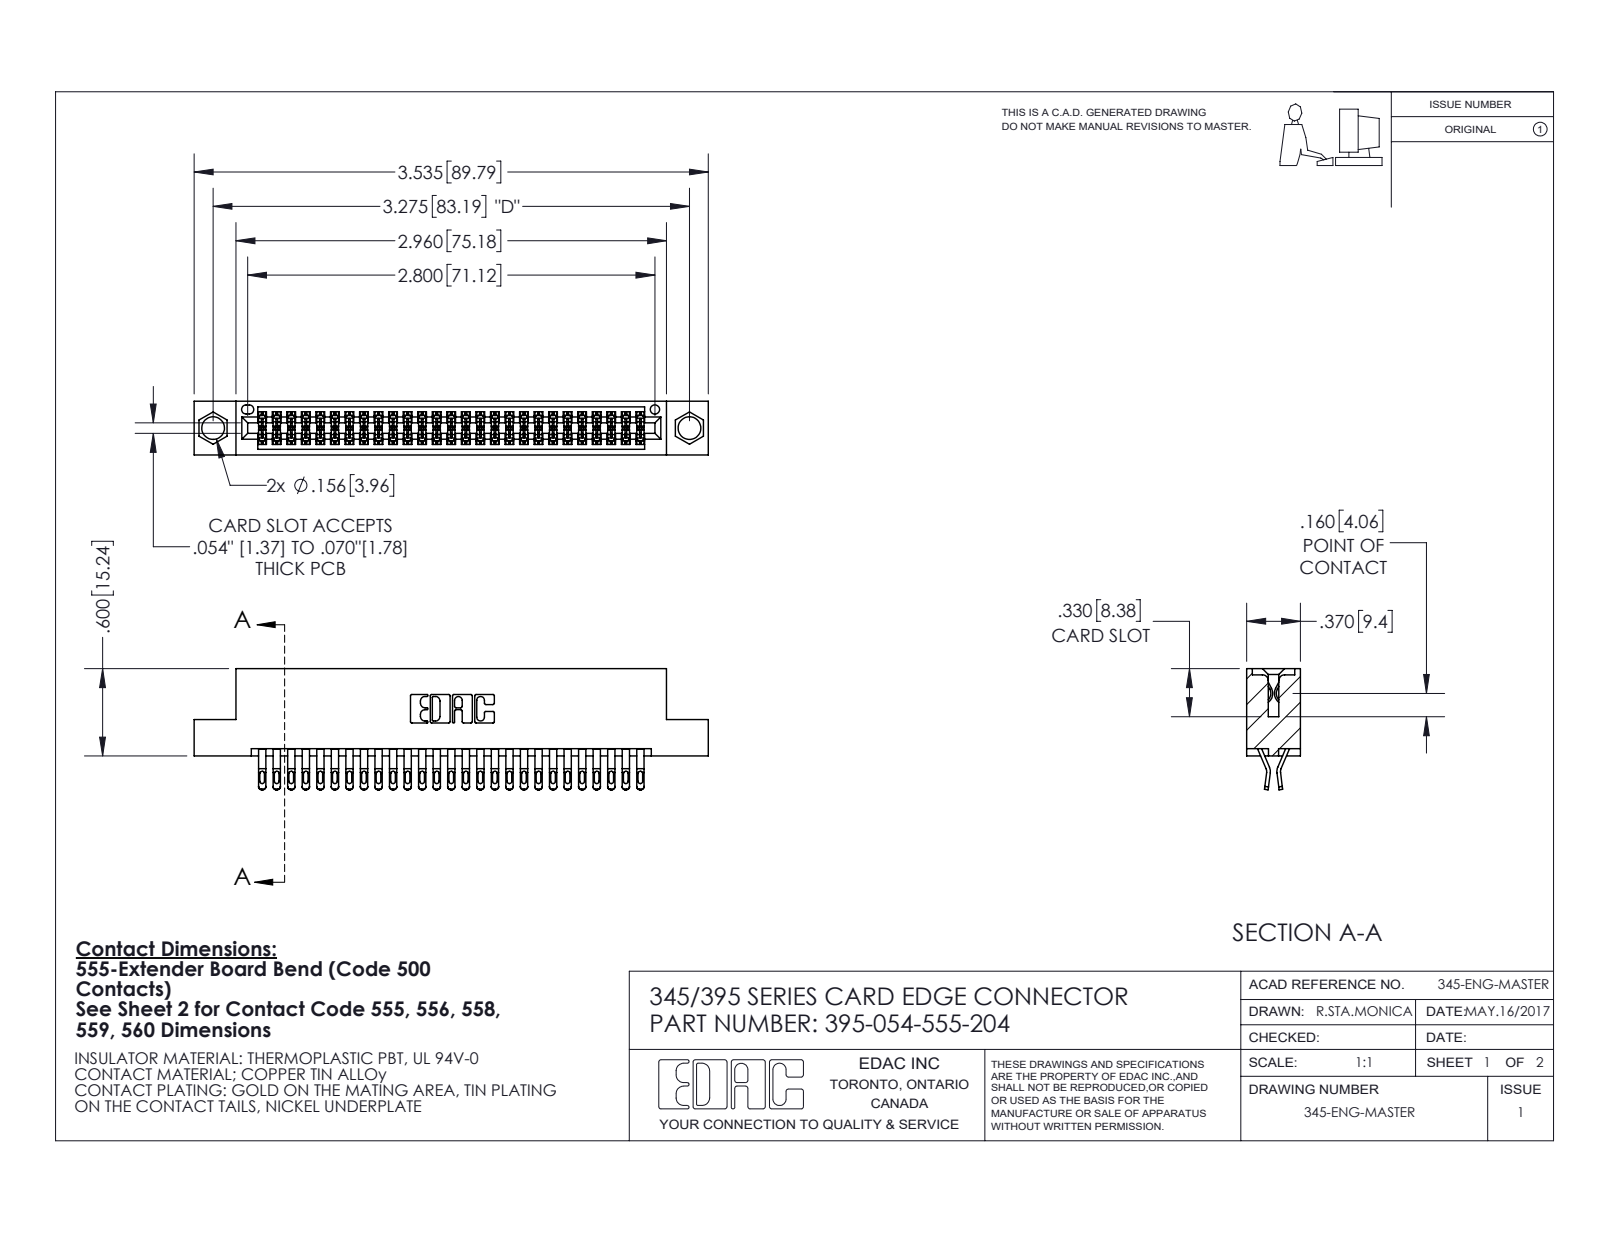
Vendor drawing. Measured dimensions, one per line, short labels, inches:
name: 395-054-555-204; 345 Part_Flush Mounting Lugs - 0.156 Dia-TI; 345-292-001_555 Tail
written by: SolidWorks 2020 (CONFIG_CONTROL_DESIGN)
unit: in
bodies: 55 solids, 3164 faces (1768 planar, 1396 cylindrical, 0 other)
size: 3.535 × 0.832 × 0.37
volume: 0.527 in³; area: 19.95 in²
holes: 2× ⌀0.156, 1× ⌀0.064
rounds: 135× R0.016, 108× R0.02, 81× R0.006, 22× R0.01, 6× R0.007, 6× R0.031, 3× R0.026, 2× R0.01
face distances: 0.298, 0.072, 0.2, 0.37, 0.025, 0.098, 0.272, 0.225, 0.175, 0.149
hole spacings: 0.27, 3.04, 3.275
